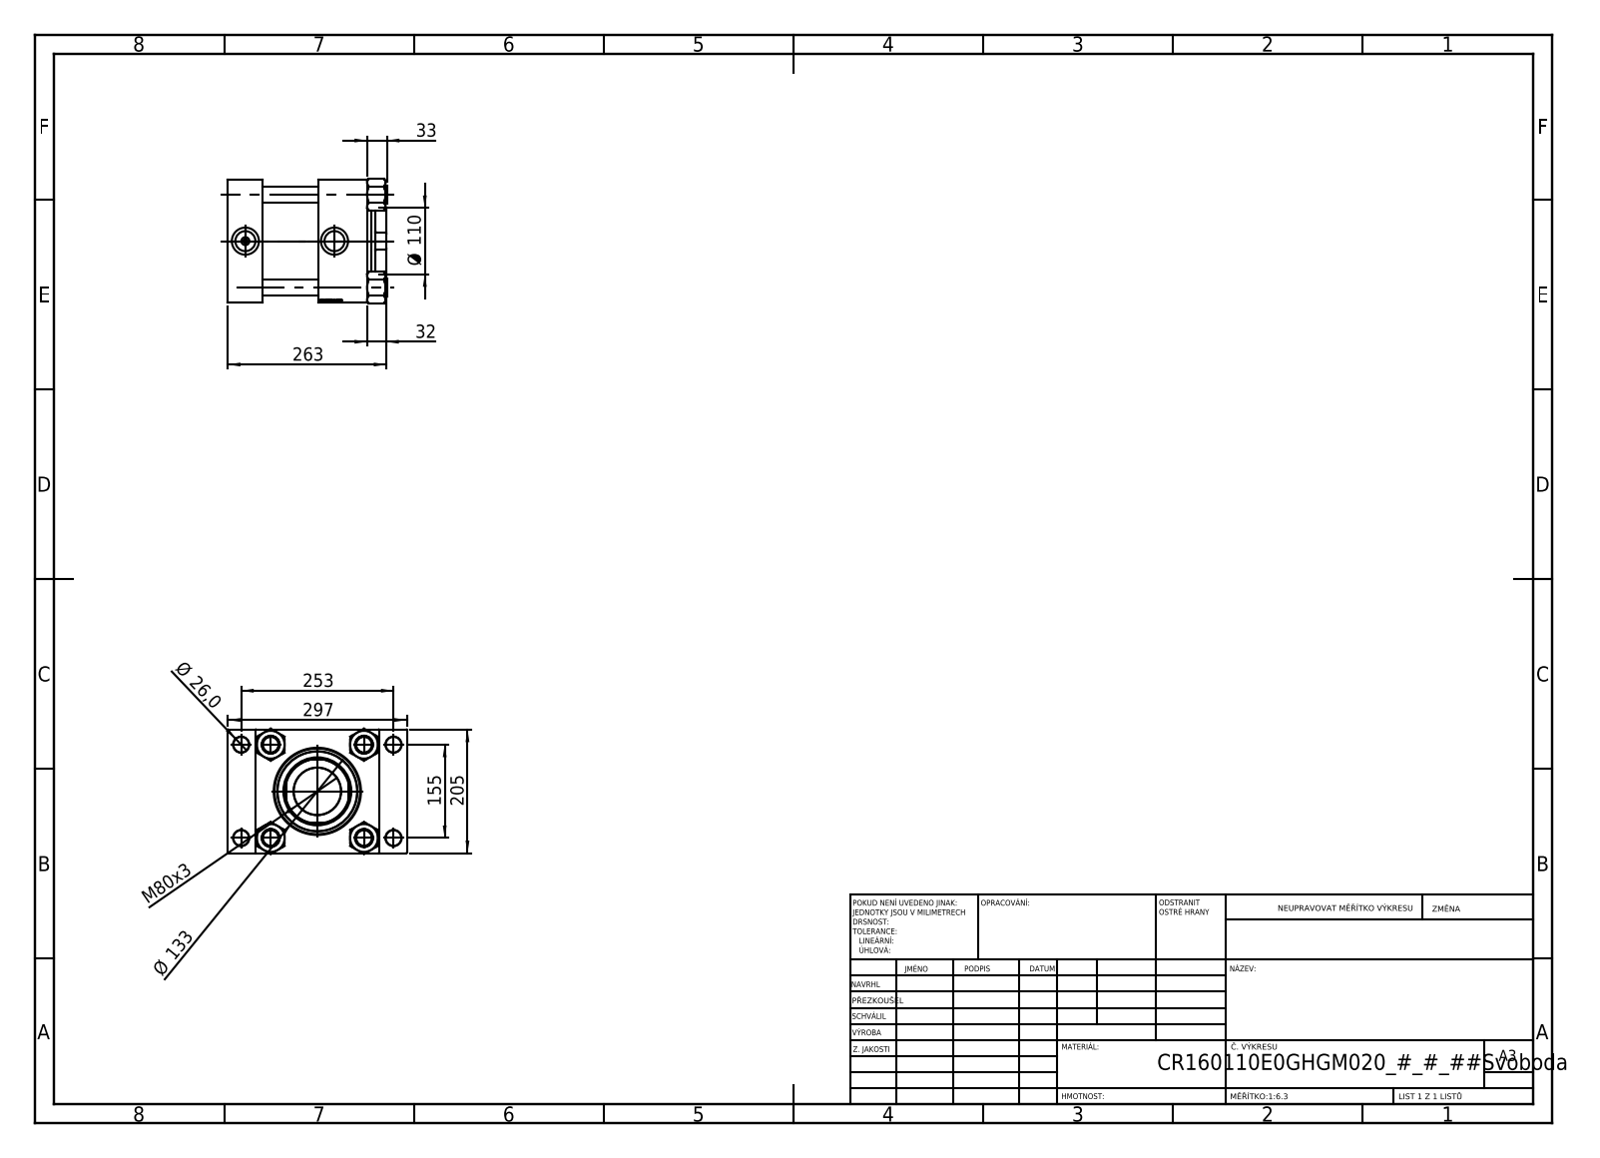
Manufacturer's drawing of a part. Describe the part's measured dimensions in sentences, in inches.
The part is named "V215CR_E_Body; V215CR_VCP_E; V215CR_TYCINKA_E; NUT_M5_E (+1 more)". Its 3-D file was written by "SolidWorks 2019 (CONFIG_CONTROL_DESIGN)". It is 11 solids with 1184 faces: 546 planar, 86 cylindrical and 552 other. Overall it measures 11.693 by 10.394 by 8.194 inches. Its volume is 526.5 cubic inches and its surface area 1 250 square inches. Round holes: 4 of diameter 1.024, 4 of diameter 1.063, 2 of diameter 0.276, 2 of diameter 1.309, 2 of diameter 1.772, 1 of diameter 3.091, 1 of diameter 4.331, 1 of diameter 4.449, 1 of diameter 4.724, 1 of diameter 5.591, 1 of diameter 6.299. Round bosses or shafts: 4 of diameter 1.181, 1 of diameter 6.535, 1 of diameter 5.236. Partial cylindrical surfaces (rounded edges, fillets, slot ends): 1 of radius 2.126. The main face-to-face distances are 2.283, 8.071, 9.094, 6.811, 5.906, 3.622, 3.189, 1.811, 9.882, 7.965. The hole center spacings are 1.931, 4.312, 5.841, 6.098, 6.399, 8.03, 10.084, 6.102.
